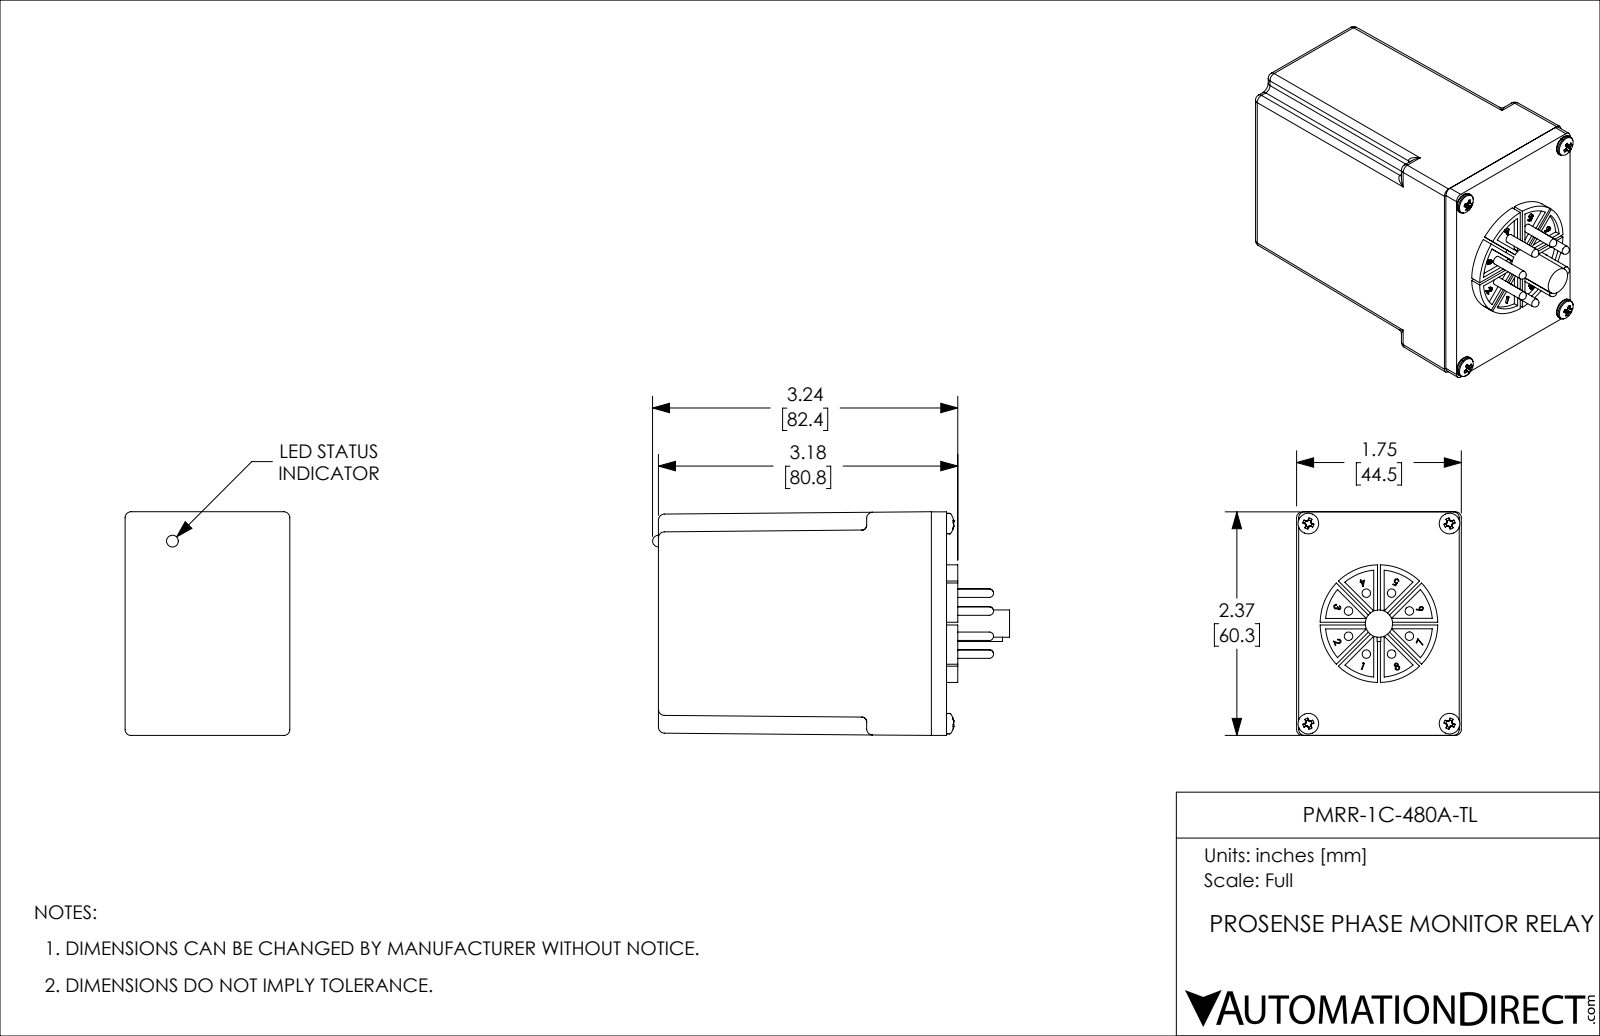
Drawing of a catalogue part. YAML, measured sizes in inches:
part_name: "PMRR-1C-480A-TL"
step_written_by: "SolidWorks 2019 (CONFIG_CONTROL_DESIGN)"
units: inches
bodies: {solids: 15, faces: 681, planar: 217, cylindrical: 280, other: 184}
overall_size: [3.792, 2.375, 1.75]
volume: 12.23
surface_area: 44.59
round_holes:
  - {diameter: 0.125, count: 4}
round_bosses_or_shafts:
  - {diameter: 0.09, count: 8}
  - {diameter: 0.219, count: 4}
  - {diameter: 0.112, count: 4}
  - {diameter: 0.08, count: 4}
  - {diameter: 1.25, count: 1}
  - {diameter: 0.29, count: 1}
partial_cylinders:
  - {radius: 0.063, count: 32}
  - {radius: 0.005, count: 8}
  - {radius: 0.05, count: 4}
  - {radius: 0.57, count: 1}
face_to_face_distances: [2.9, 0.16, 3.06, 0.07, 0.23, 3.13, 0.188, 0.05, 0.12, 0.28]
hole_center_spacings: [1.5, 2.125, 2.601]
